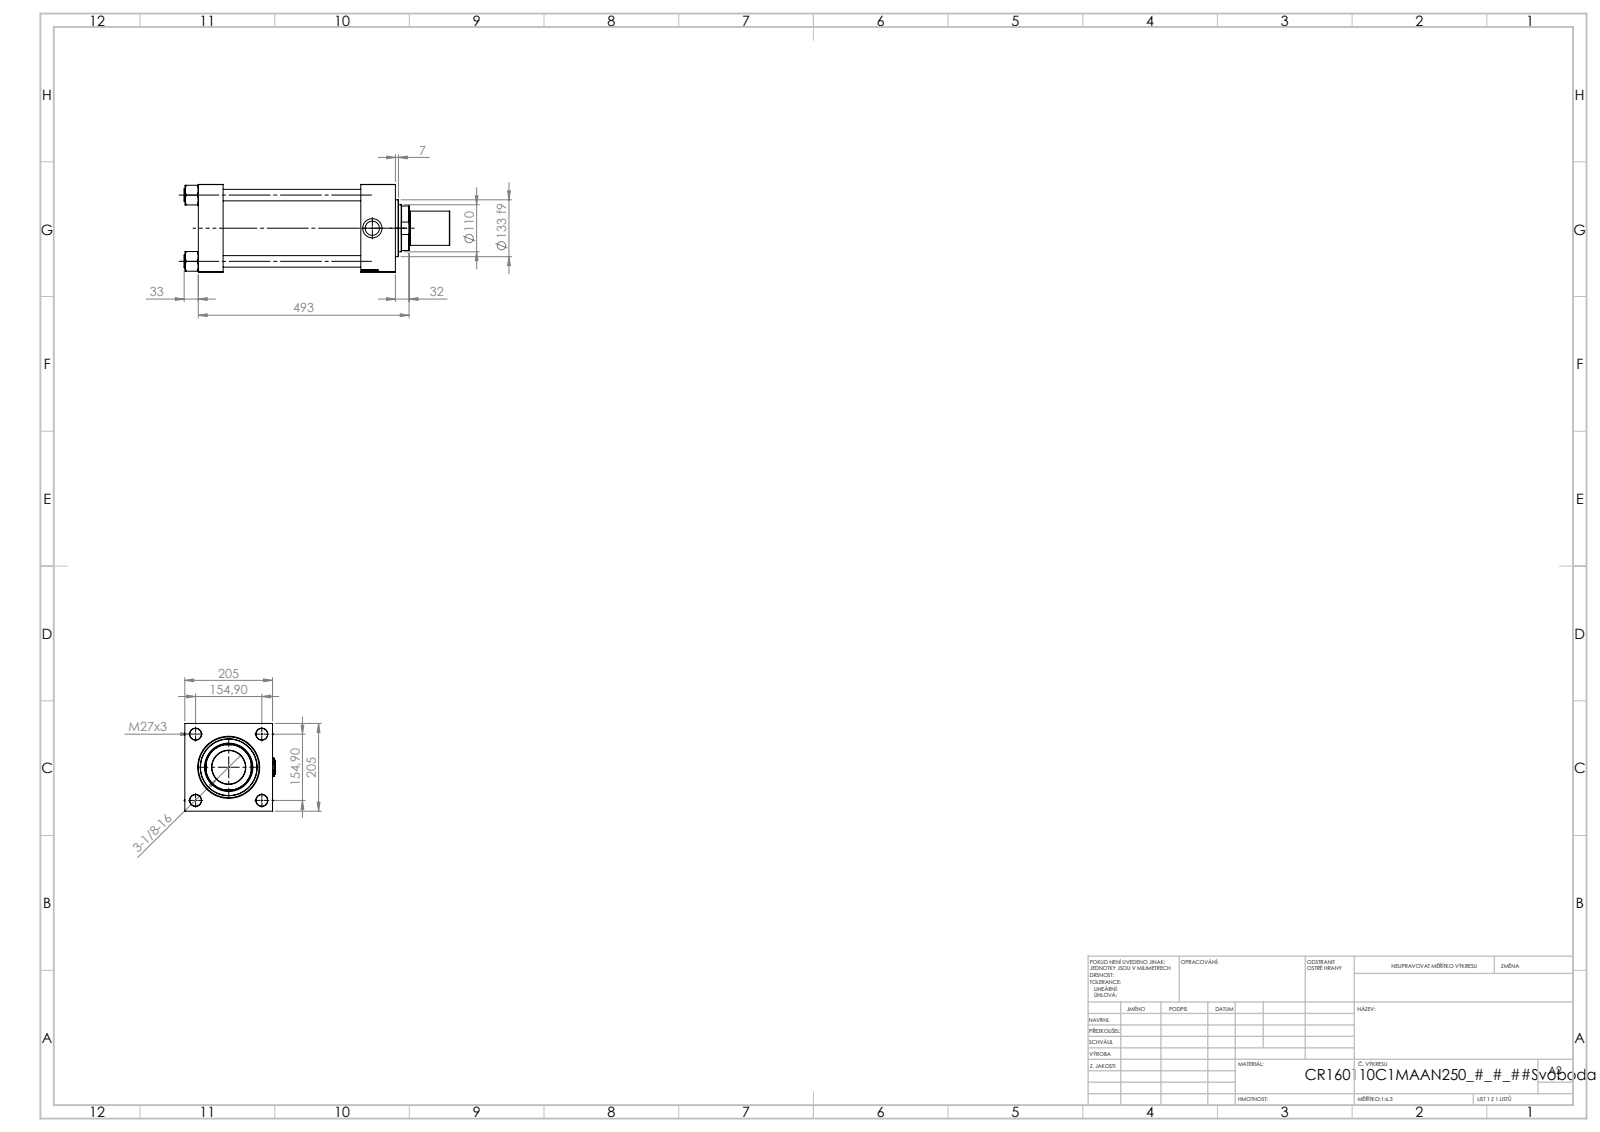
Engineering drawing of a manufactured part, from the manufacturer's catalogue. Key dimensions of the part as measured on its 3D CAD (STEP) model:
Part name (STEP PRODUCT): V215CR_C_TYCINKA; V215CR_C_Body; ROD_END_AH; V215_VC_A (+3 more)
STEP written by: SolidWorks 2019 (CONFIG_CONTROL_DESIGN)
Units: millimetres
Bodies: 13 solids, 1258 faces (601 planar, 95 cylindrical, 562 other)
Overall size (bounding box): 621 × 213.57 × 205
Volume: 11 160 000 mm³ · Surface area: 1 154 000 mm²
Round holes (diameter × count): ⌀27 ×4, ⌀7 ×2, ⌀33.24 ×2, ⌀45 ×2, ⌀78.5 ×1, ⌀110 ×1, ⌀113 ×1, ⌀120 ×1, ⌀142 ×1, ⌀160 ×1
Round bosses / shafts (diameter × count): ⌀30 ×4, ⌀166 ×1, ⌀133 ×1, ⌀80 ×1, ⌀78 ×1
Partial cylindrical surfaces — rounded edges, fillets, slot ends (radius × count): R54 ×1
Main face-to-face distances: 205, 58, 380, 322, 461, 403, 81, 432.3, 374.3, 52.3
Hole centre spacings: 109.53, 154.9, 219.06
